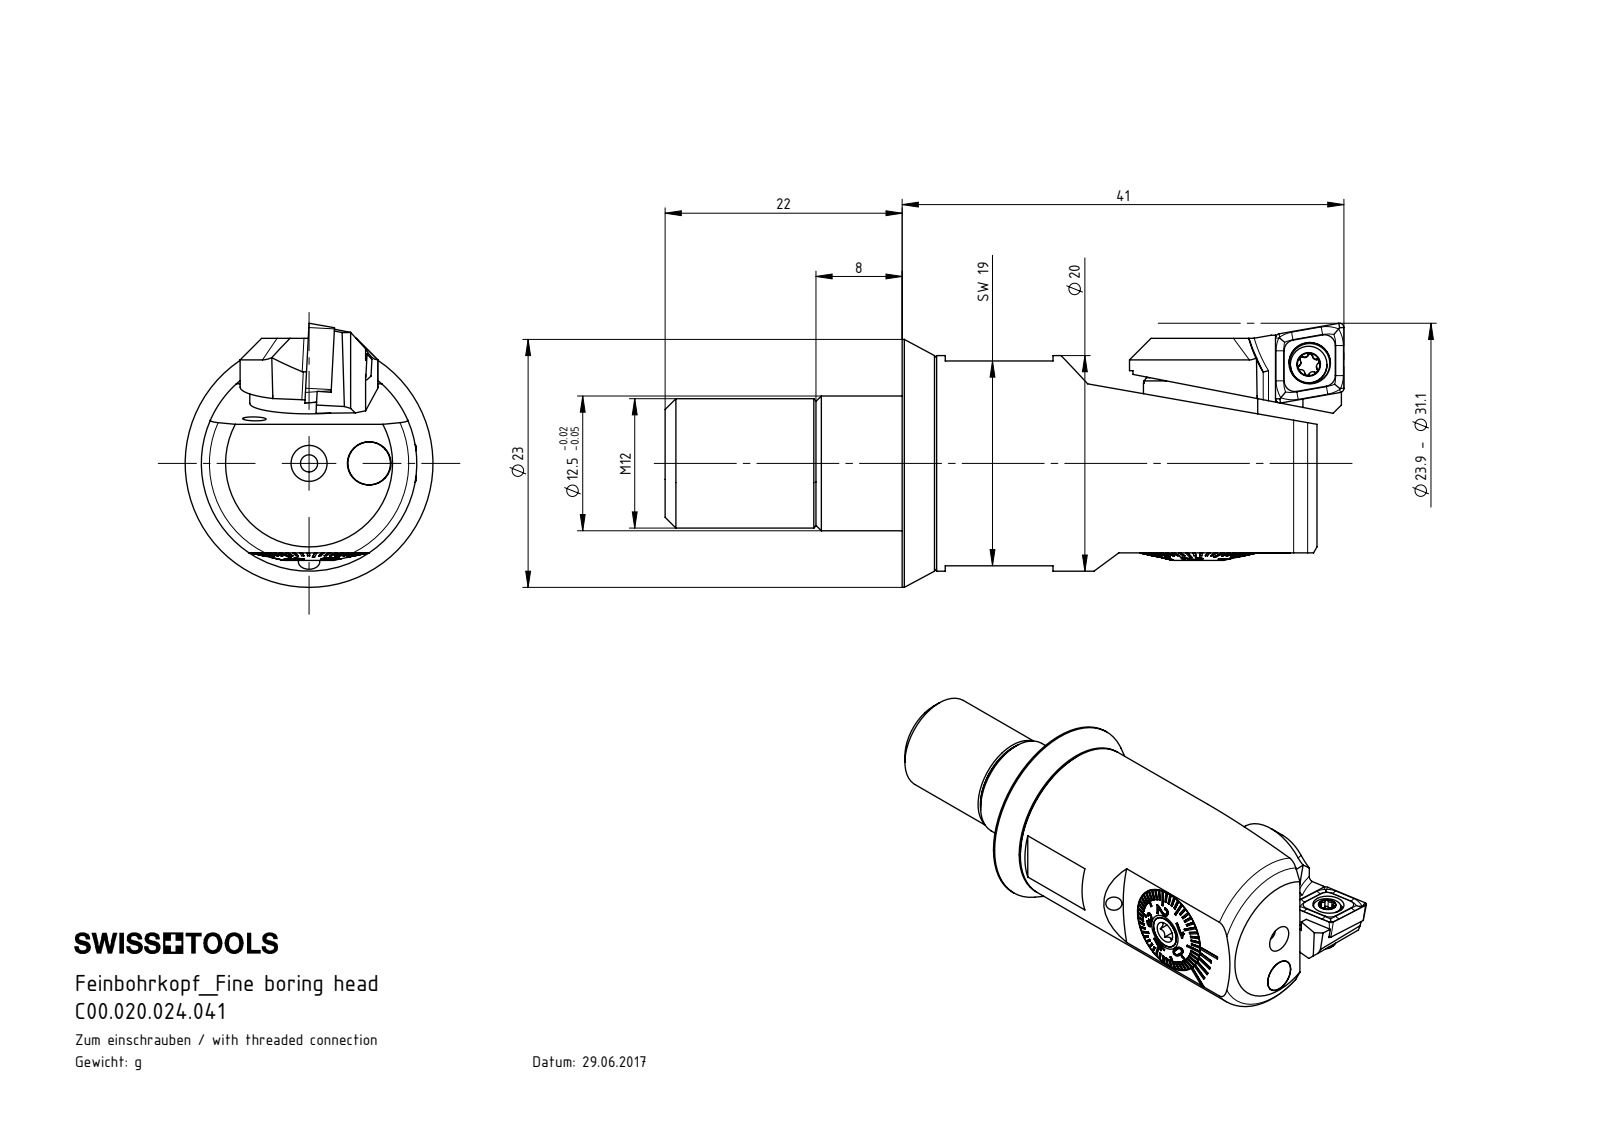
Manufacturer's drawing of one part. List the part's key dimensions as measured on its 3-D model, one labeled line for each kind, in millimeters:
Part name (STEP PRODUCT): F20-BG2.011.003_A; C00.020.024.041; F20-WCA.001.005; F20 (+8 more)
STEP written by: SolidWorks 2017 (CONFIG_CONTROL_DESIGN)
Units: millimetres
Bodies: 17 solids, 787 faces (338 planar, 148 cylindrical, 301 other)
Overall size (bounding box): 63 × 23.35 × 23
Volume: 13 060 mm³ · Surface area: 10 102 mm²
Round holes (diameter × count): ⌀2 ×4, ⌀3.3 ×3, ⌀1.6 ×1, ⌀1.9 ×1, ⌀2.05 ×1, ⌀2.5 ×1, ⌀2.8 ×1, ⌀3 ×1, ⌀3.85 ×1, ⌀4 ×1, ⌀4.5 ×1, ⌀5.4 ×1
Round bosses / shafts (diameter × count): ⌀4 ×2, ⌀3.95 ×2, ⌀23 ×1, ⌀20 ×1, ⌀12 ×1, ⌀10.98 ×1, ⌀10.85 ×1, ⌀8.65 ×1
Partial cylindrical surfaces — rounded edges, fillets, slot ends (radius × count): R0.21 ×6, R0.36 ×5, R0.3 ×2, R0.5 ×2, R2 ×2, R3 ×2, R5 ×2, R0.36 ×1
Main face-to-face distances: 3, 6, 38.5, 35.5, 15.1, 11.35, 3.75, 8, 11, 46.5
Hole centre spacings: 5.6, 7, 12.6, 14
